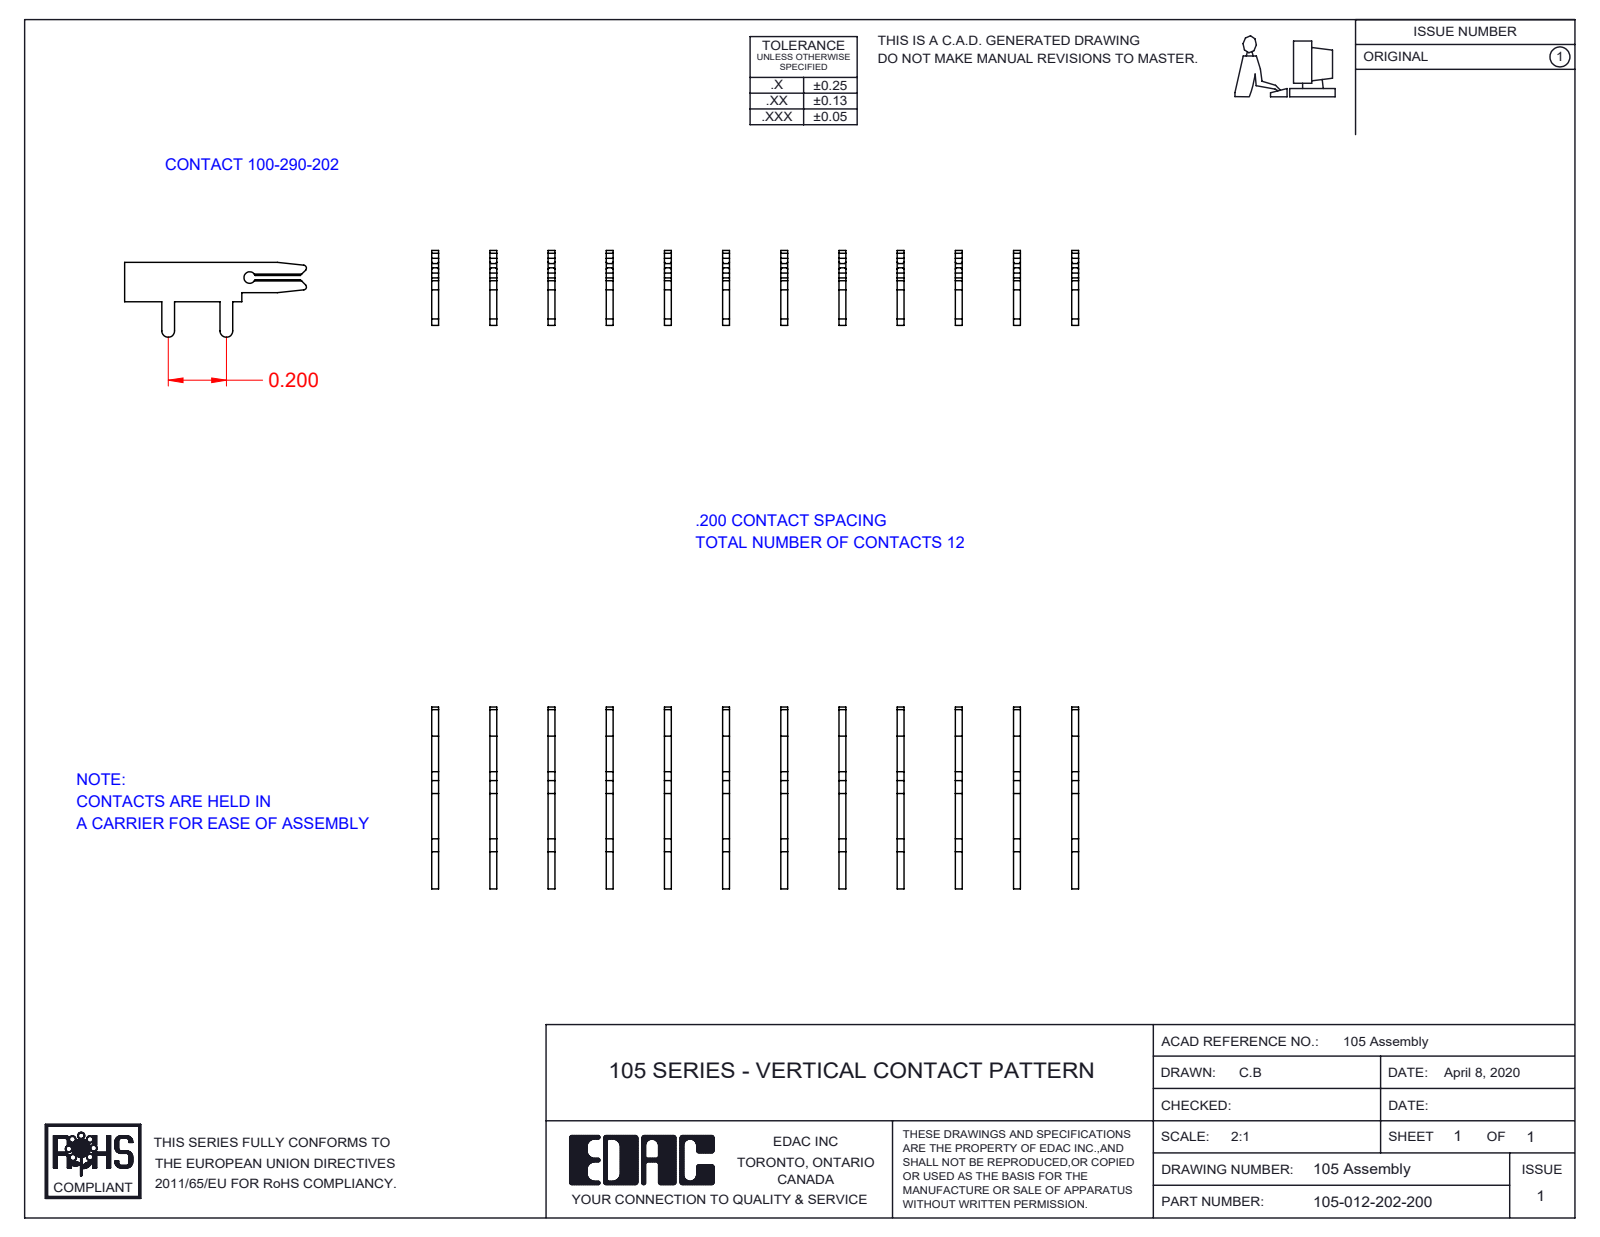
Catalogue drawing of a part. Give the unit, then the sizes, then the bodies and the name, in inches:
Units: inches
Overall size (bounding box): 2.224 × 0.625 × 0.257
Round holes (diameter × count): ⌀0.04 ×1
Partial cylindrical surfaces — rounded edges, fillets, slot ends (radius × count): R0.01 ×2, R0.022 ×2
Main face-to-face distances: 0.2, 0.4, 0.6, 0.8, 1, 1.2, 0.024, 0.224, 0.424, 0.624
Volume: 0.023 in³ · Surface area: 2.628 in²
Bodies: 12 solids, 360 faces (276 planar, 84 cylindrical, 0 other)
Part name (STEP PRODUCT): 105-012-202-200; 100-290-001_100-290-202
STEP written by: SolidWorks 2016 (CONFIG_CONTROL_DESIGN)
